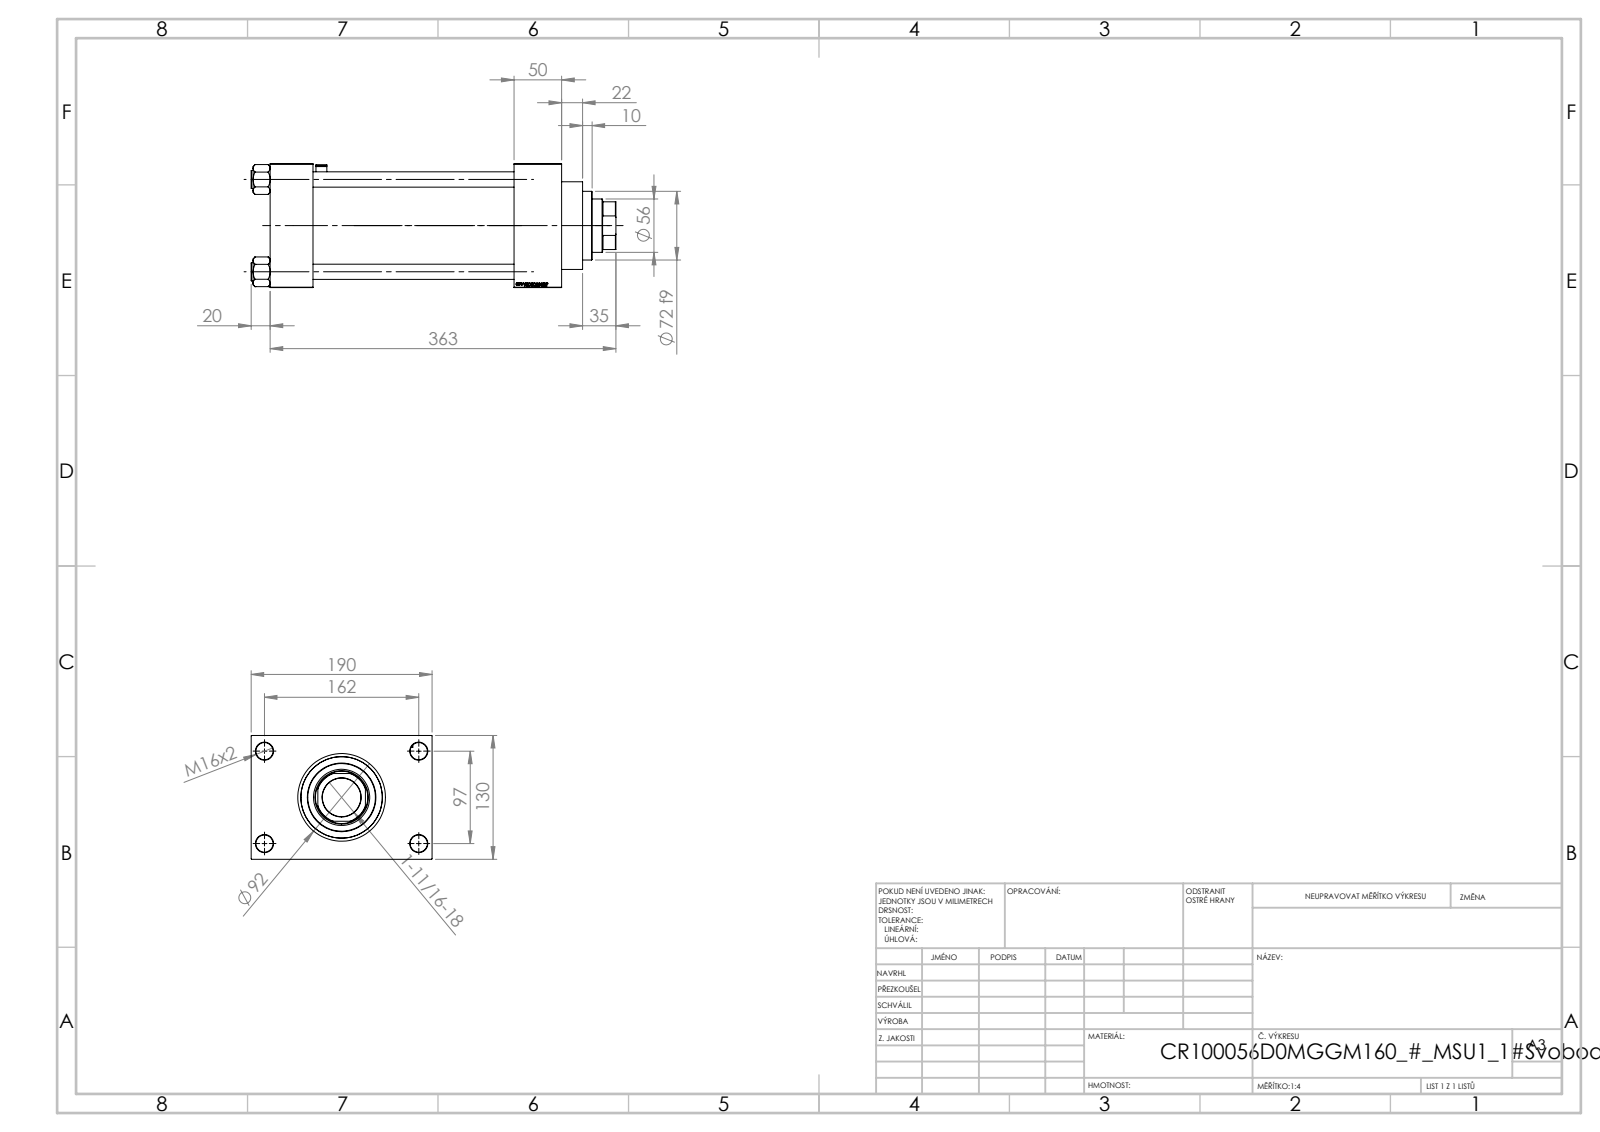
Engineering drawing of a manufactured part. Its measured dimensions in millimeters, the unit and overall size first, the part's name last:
Units: millimetres
Overall size (bounding box): 383 × 190 × 130
Round holes (diameter × count): ⌀16 ×4, ⌀18 ×4, ⌀7 ×2, ⌀26.44 ×2, ⌀35 ×2, ⌀40.5 ×1, ⌀56 ×1, ⌀59 ×1, ⌀76 ×1, ⌀85.5 ×1, ⌀100 ×1
Round bosses / shafts (diameter × count): ⌀19 ×4, ⌀106 ×1, ⌀92 ×1, ⌀72 ×1, ⌀6 ×1
Partial cylindrical surfaces — rounded edges, fillets, slot ends (radius × count): R0.5 ×24, R1 ×1, R2.5 ×1, R4 ×1, R27 ×1
Main face-to-face distances: 130, 50, 45, 256, 211, 160, 306, 261, 30, 190
Hole centre spacings: 32.55, 68.52, 94.41, 96.9, 102.27, 129.45, 161.73, 97
Volume: 3 258 000 mm³ · Surface area: 509 488 mm²
Bodies: 12 solids, 1229 faces (574 planar, 119 cylindrical, 536 other)
Part name (STEP PRODUCT): V215CR_VCP_D; NUT_M5_D; V215_VC_A; V215CR_D_TYCINKA (+2 more)
STEP written by: SolidWorks 2019 (CONFIG_CONTROL_DESIGN)
